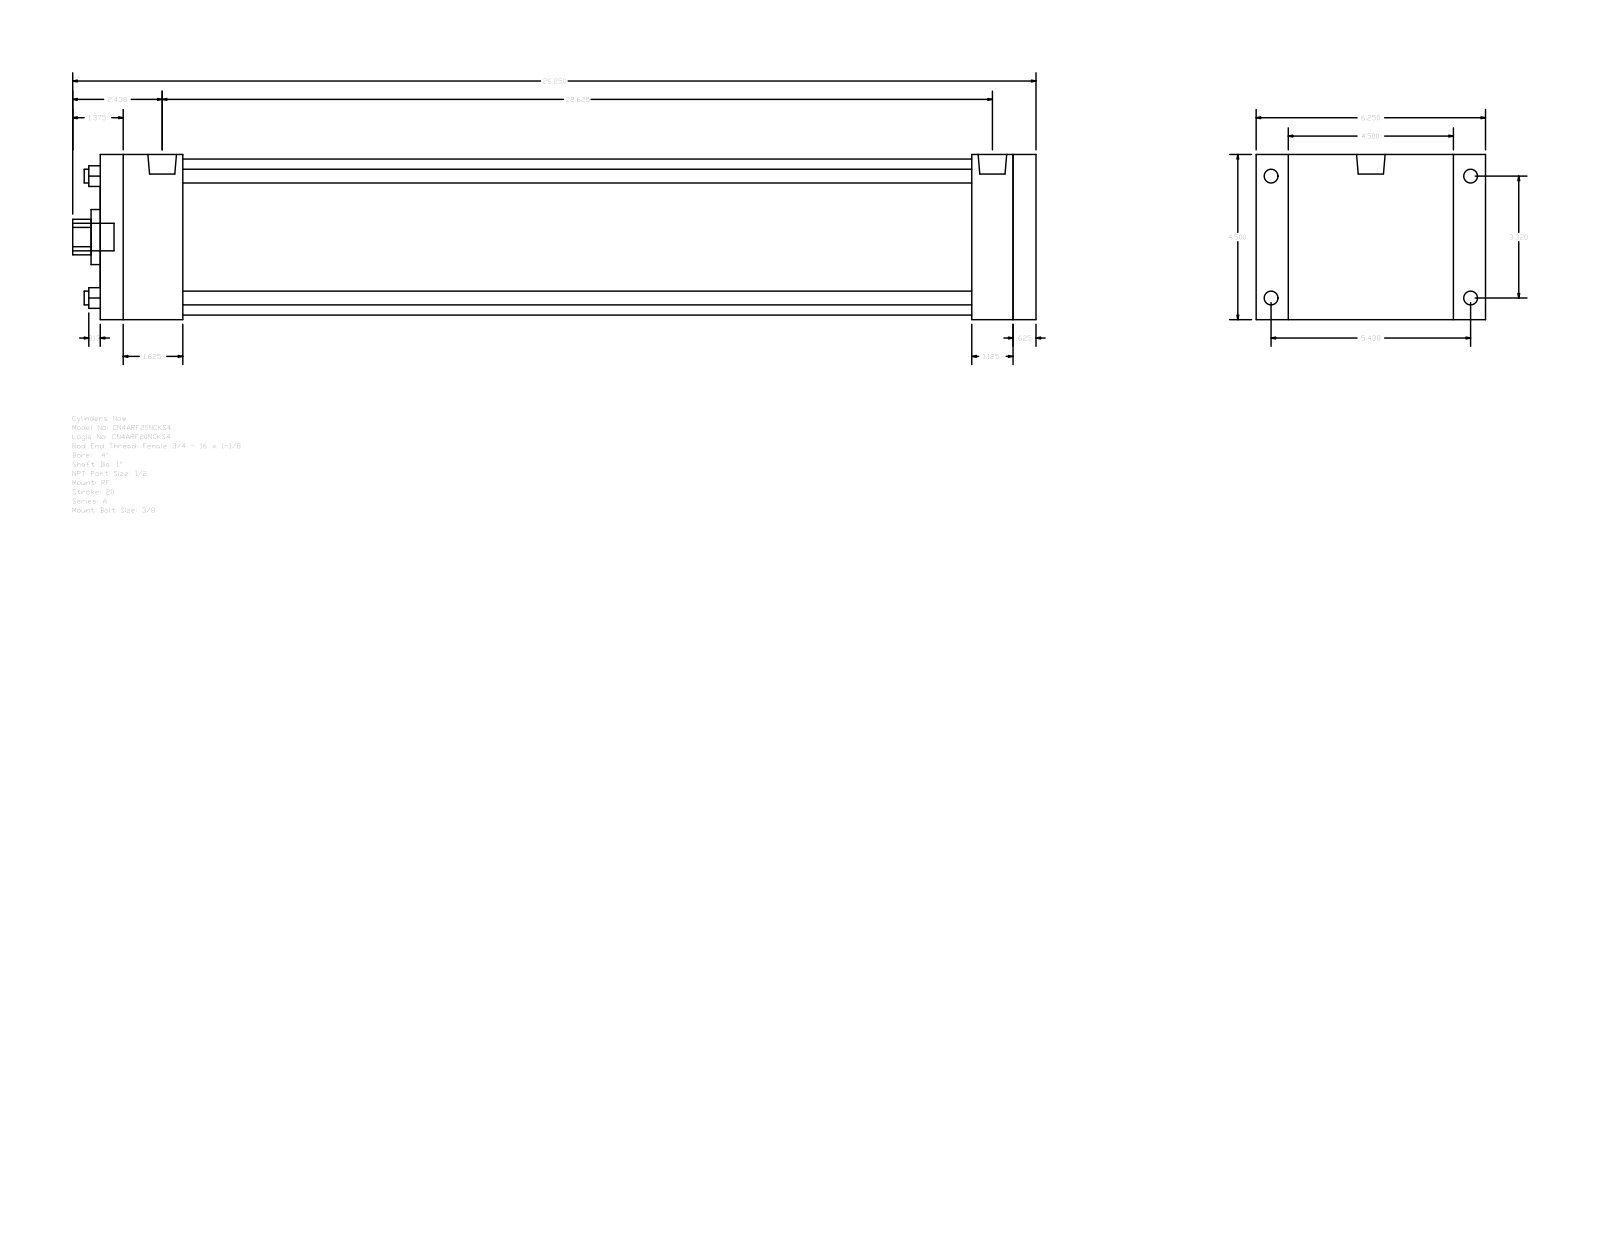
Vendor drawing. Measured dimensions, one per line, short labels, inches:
name: A_RF__0400_1
written by: GSSL Pune (CONFIG_CONTROL_DESIGN)
unit: in
bodies: 0 solids, 92 faces (64 planar, 28 cylindrical, 0 other)
size: 26.25 × 6.25 × 4.5
holes: 4× ⌀0.375, 1× ⌀1, 1× ⌀1.5, 1× ⌀4.25
bosses: 4× ⌀0.375, 4× ⌀0.344, 2× ⌀0.778, 1× ⌀0.75
rounds: 1× R0.484
face distances: 4.5, 25.5, 0.625, 24.875, 0.875, 5.375, 23.75, 1.125, 1.75, 2.25
hole spacings: 2.347, 3.32, 4.695
